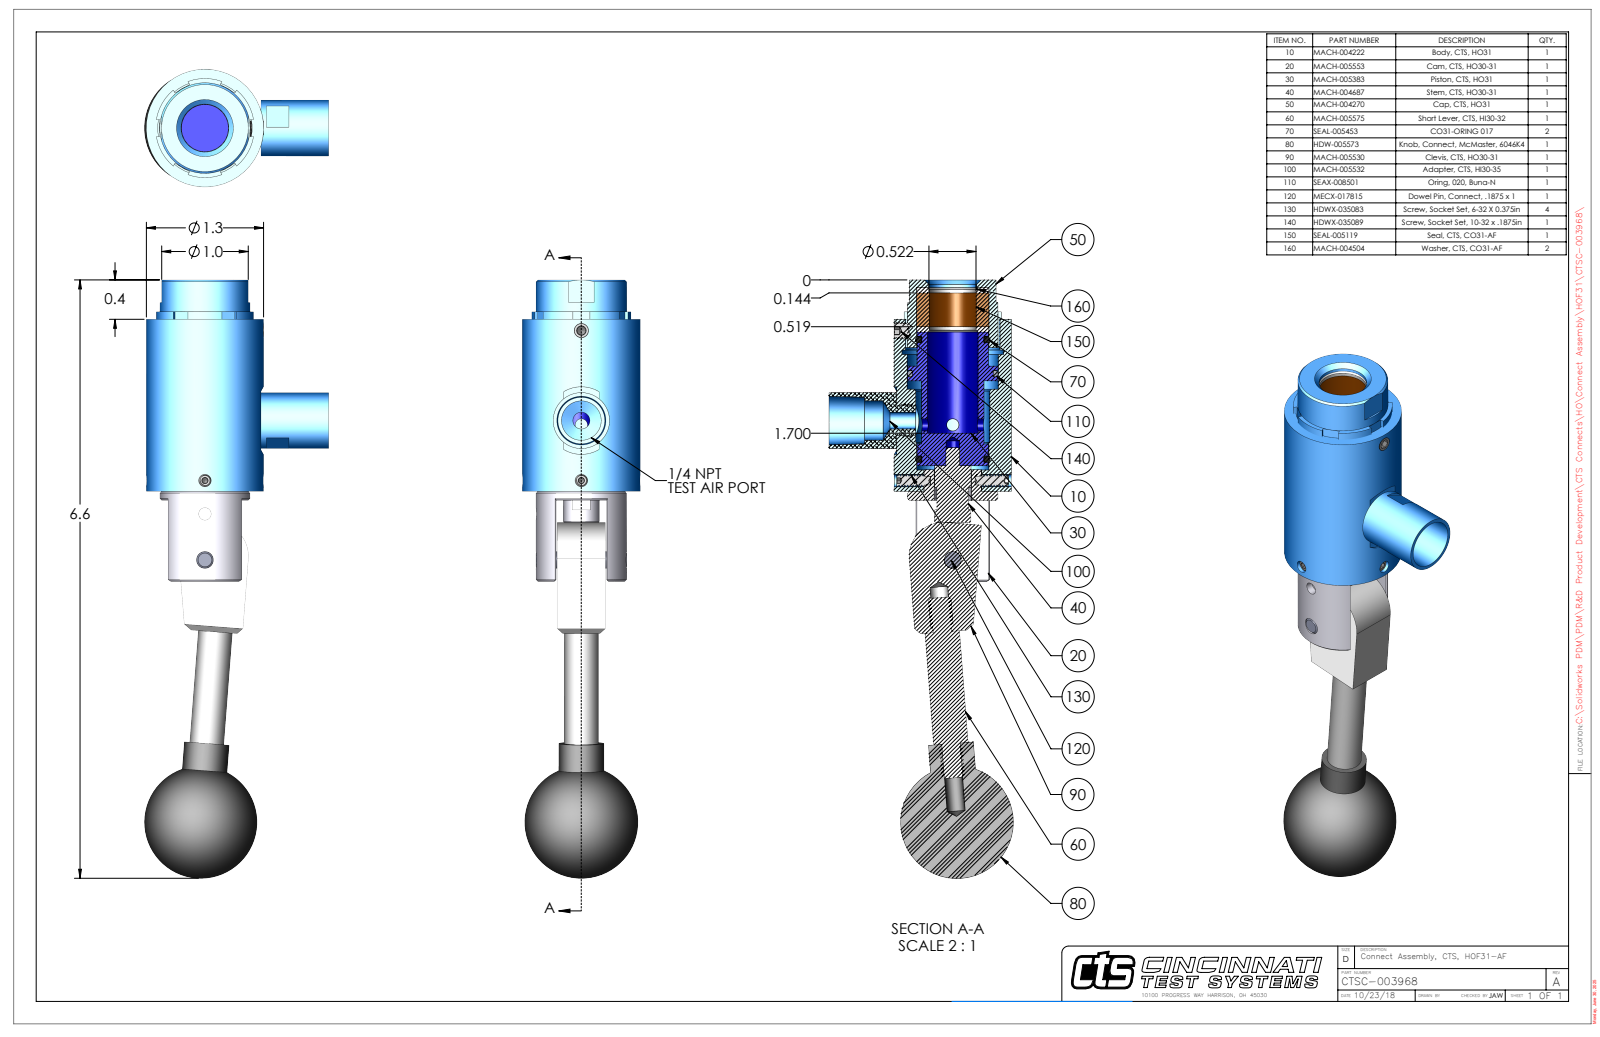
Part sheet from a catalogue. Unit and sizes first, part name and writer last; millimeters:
Units: millimetres
Overall size (bounding box): 168.6 × 51.9 × 33
Round holes (diameter × count): ⌀3.5 ×2, ⌀5.1 ×2, ⌀3.5 ×1, ⌀3.8 ×1, ⌀4 ×1, ⌀4.7 ×1, ⌀4.8 ×1, ⌀4.8 ×1, ⌀8.4 ×1, ⌀10.6 ×1, ⌀11.1 ×1, ⌀13.3 ×1
Round bosses / shafts (diameter × count): ⌀3.5 ×2, ⌀33 ×1, ⌀25.4 ×1, ⌀20.1 ×1, ⌀20.1 ×1, ⌀17.5 ×1, ⌀16 ×1, ⌀15.7 ×1
Partial cylindrical surfaces — rounded edges, fillets, slot ends (radius × count): R9.5 ×1, R9.5 ×1, R13.3 ×1, R13.9 ×1
Main face-to-face distances: 0.3, 13.8, 1.5, 11, 13.5, 14.1, 46.4, 55.9, 9.5, 13.2
Hole centre spacings: 1.2, 13, 25.1, 25.3, 26.5, 38
Volume: 73 250 mm³ · Surface area: 29 850 mm²
Bodies: 14 solids, 532 faces (173 planar, 217 cylindrical, 142 other)
Part name (STEP PRODUCT): CTSC-003968
STEP written by: SolidWorks 2023 (AUTOMOTIVE_DESIGN)
